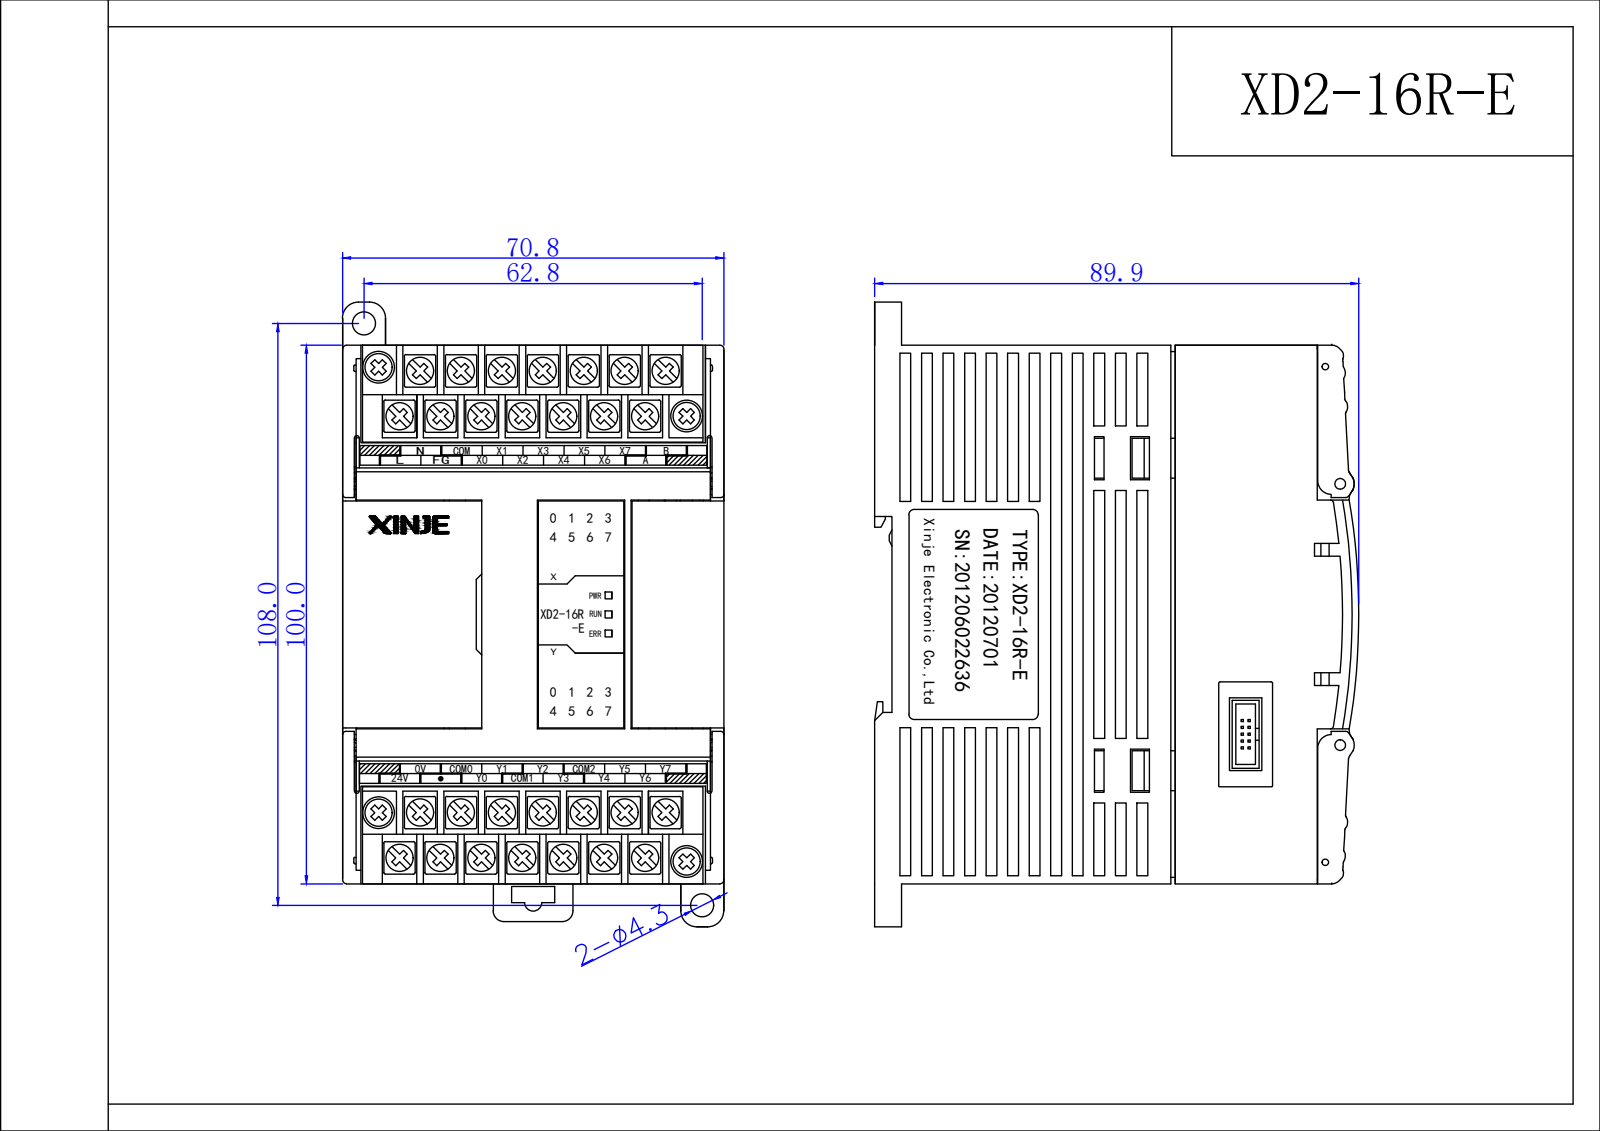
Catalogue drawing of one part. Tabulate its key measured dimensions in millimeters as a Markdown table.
| quantity | value |
| --- | --- |
| STEP written by | ST-DEVELOPER v16.5 (CONFIG_CONTROL_DESIGN) |
| units | millimeters |
| bodies | 2 solids, 3095 faces (2085 planar, 689 cylindrical, 321 other) |
| overall size | 116 × 89.69 × 70.6 |
| volume | 576 100 mm³ |
| surface area | 70 260 mm² |
| round holes (diameter × count) | 3.45 × 28, 4.3 × 2 |
| round bosses / shafts (diameter × count) | 5.4 × 32, 3 × 28, 2.5 × 28 |
| partial cylindrical surfaces (radius × count) | 0.25 × 112, 0.2 × 60, 0.5 × 16, 0.75 × 8, 1 × 8, 0.1 × 4, 0.3 × 4, 0.45 × 4 |
| main face-to-face distances | 70.6, 70.3, 3.2, 100, 18.1, 81.9, 2.2, 68.1, 62.71, 0.75 |
| hole center spacings | 9.22, 7.6, 82.35, 15.2, 83.4, 22.8, 85.11, 82 |
